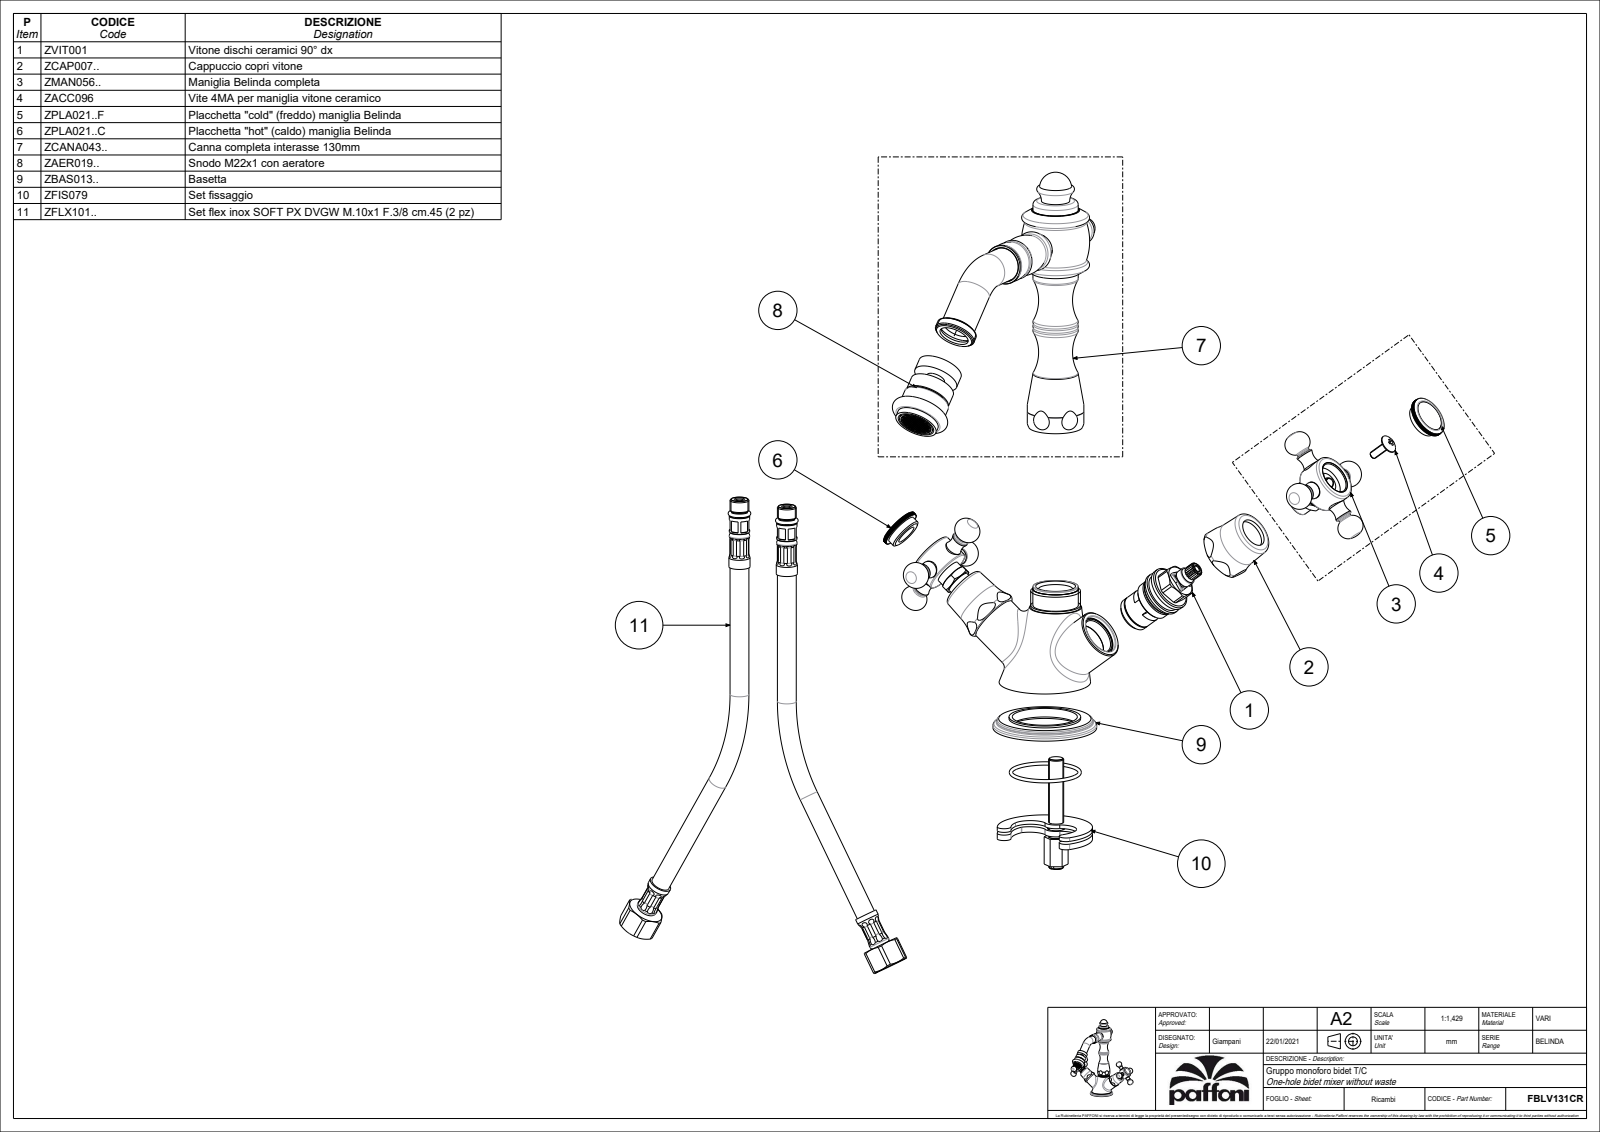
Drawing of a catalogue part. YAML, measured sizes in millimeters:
part_name: "FBLV131CR"
step_written_by: "CREO PARAMETRIC BY PTC INC, 2020044 (CONFIG_CONTROL_DESIGN)"
units: millimeters
bodies: {solids: 3, faces: 1331, planar: 579, cylindrical: 398, other: 354}
overall_size: [229.4, 175.57, 174.66]
volume: 225192
surface_area: 68750
round_holes:
  - {diameter: 9, count: 4}
  - {diameter: 11, count: 2}
  - {diameter: 15.5, count: 2}
  - {diameter: 18, count: 2}
  - {diameter: 19, count: 2}
  - {diameter: 21, count: 2}
  - {diameter: 21.5, count: 2}
  - {diameter: 22.8, count: 2}
  - {diameter: 25.5, count: 2}
  - {diameter: 6, count: 1}
  - {diameter: 6.8, count: 1}
  - {diameter: 10, count: 1}
round_bosses_or_shafts:
  - {diameter: 9, count: 6}
  - {diameter: 7, count: 6}
  - {diameter: 25, count: 3}
  - {diameter: 26.3, count: 2}
  - {diameter: 24, count: 2}
  - {diameter: 18, count: 2}
  - {diameter: 14, count: 2}
  - {diameter: 13, count: 2}
partial_cylinders:
  - {radius: 3.5, count: 2}
  - {radius: 11, count: 2}
face_to_face_distances: [5, 4.98, 2, 1.3, 57.21, 11.4, 45.81, 1, 29.2, 24.2]
hole_center_spacings: [7, 13.38, 13.89, 0.6, 11.4, 12, 14]
